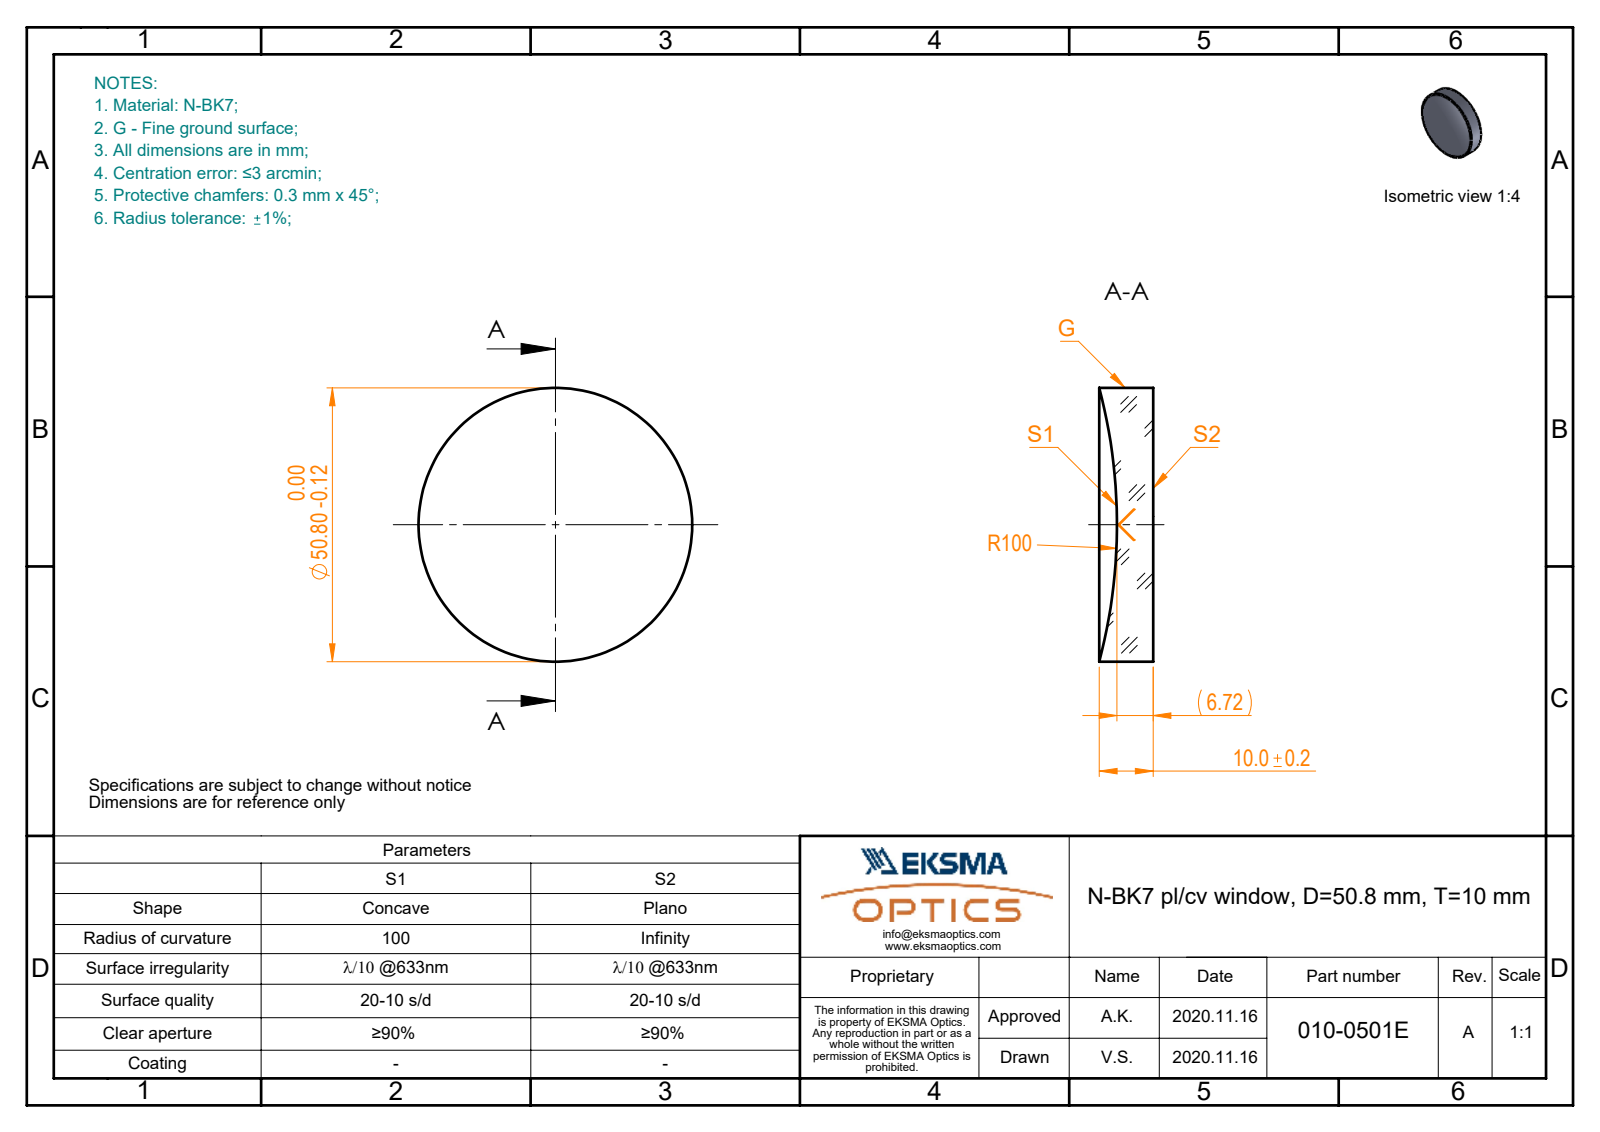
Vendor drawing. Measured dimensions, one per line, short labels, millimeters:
name: 010-0501E_N-BK7_PCV_window
written by: SolidWorks 2019 (CONFIG_CONTROL_DESIGN)
unit: mm
bodies: 1 solid, 5 faces (1 planar, 2 cylindrical, 2 other)
size: 50.8 × 50.8 × 10
volume: 16 926 mm³; area: 5 683 mm²
bosses: 1× ⌀50.8
